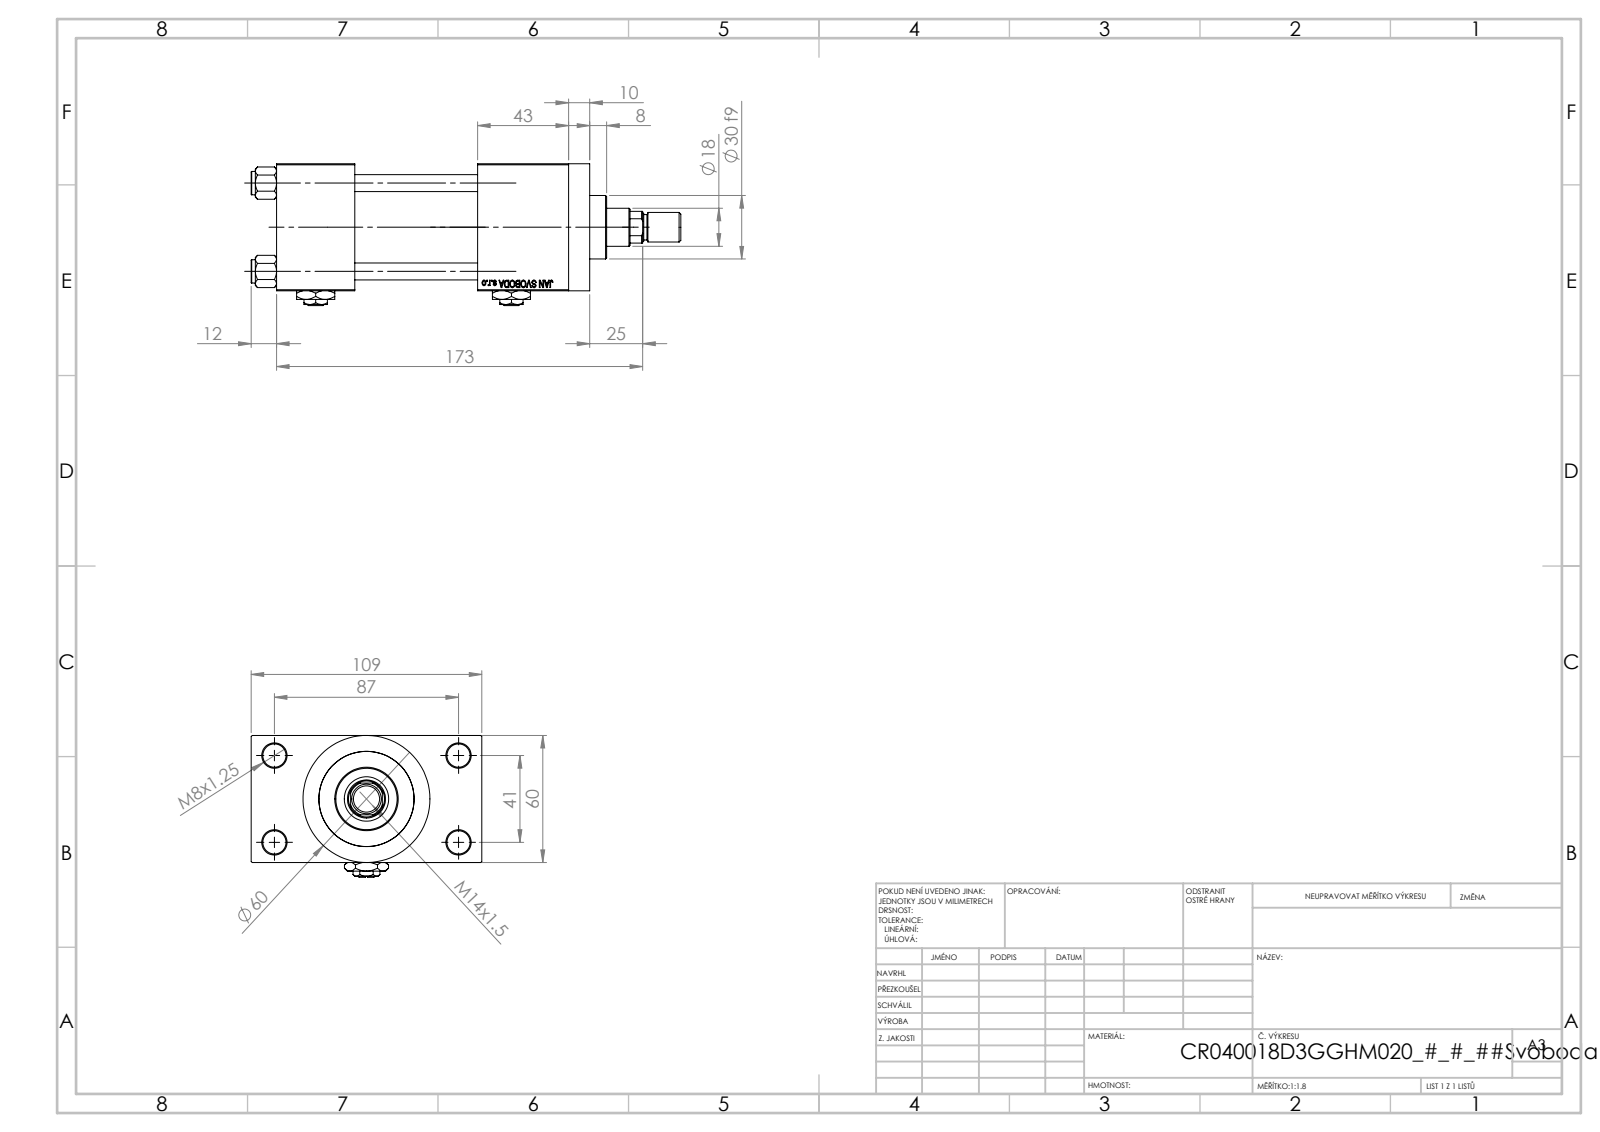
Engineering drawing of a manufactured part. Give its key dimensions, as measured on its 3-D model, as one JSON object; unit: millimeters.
{"part_name": "V215CR_VCP_D; NUT_M5_D; V215CR_D_TYCINKA; Zatka_pro_OIL_PORT (+3 more)", "step_written_by": "SolidWorks 2019 (CONFIG_CONTROL_DESIGN)", "units": "millimeters", "bodies": {"solids": 14, "faces": 1220, "planar": 550, "cylindrical": 104, "other": 566}, "overall_size": [203, 109, 67], "volume_mm3": 518264, "surface_area_mm2": 125041, "round_holes": [[8, 4], [11, 4], [7, 2], [16.66, 2], [24, 2], [8.5, 1], [18, 1], [21, 1], [31, 1], [40, 1], [45, 1]], "round_bosses_or_shafts": [[11, 4], [60, 1], [46, 1], [30, 1], [14, 1], [12, 1]], "partial_cylinders_radius": [[8.5, 1]], "face_to_face_distances": [60, 24.5, 84.5, 58, 37, 95, 43, 138, 101, 109], "hole_center_spacings": [22.65, 29.49, 41.7, 47.15, 48.09, 64.35, 76.49, 41]}
